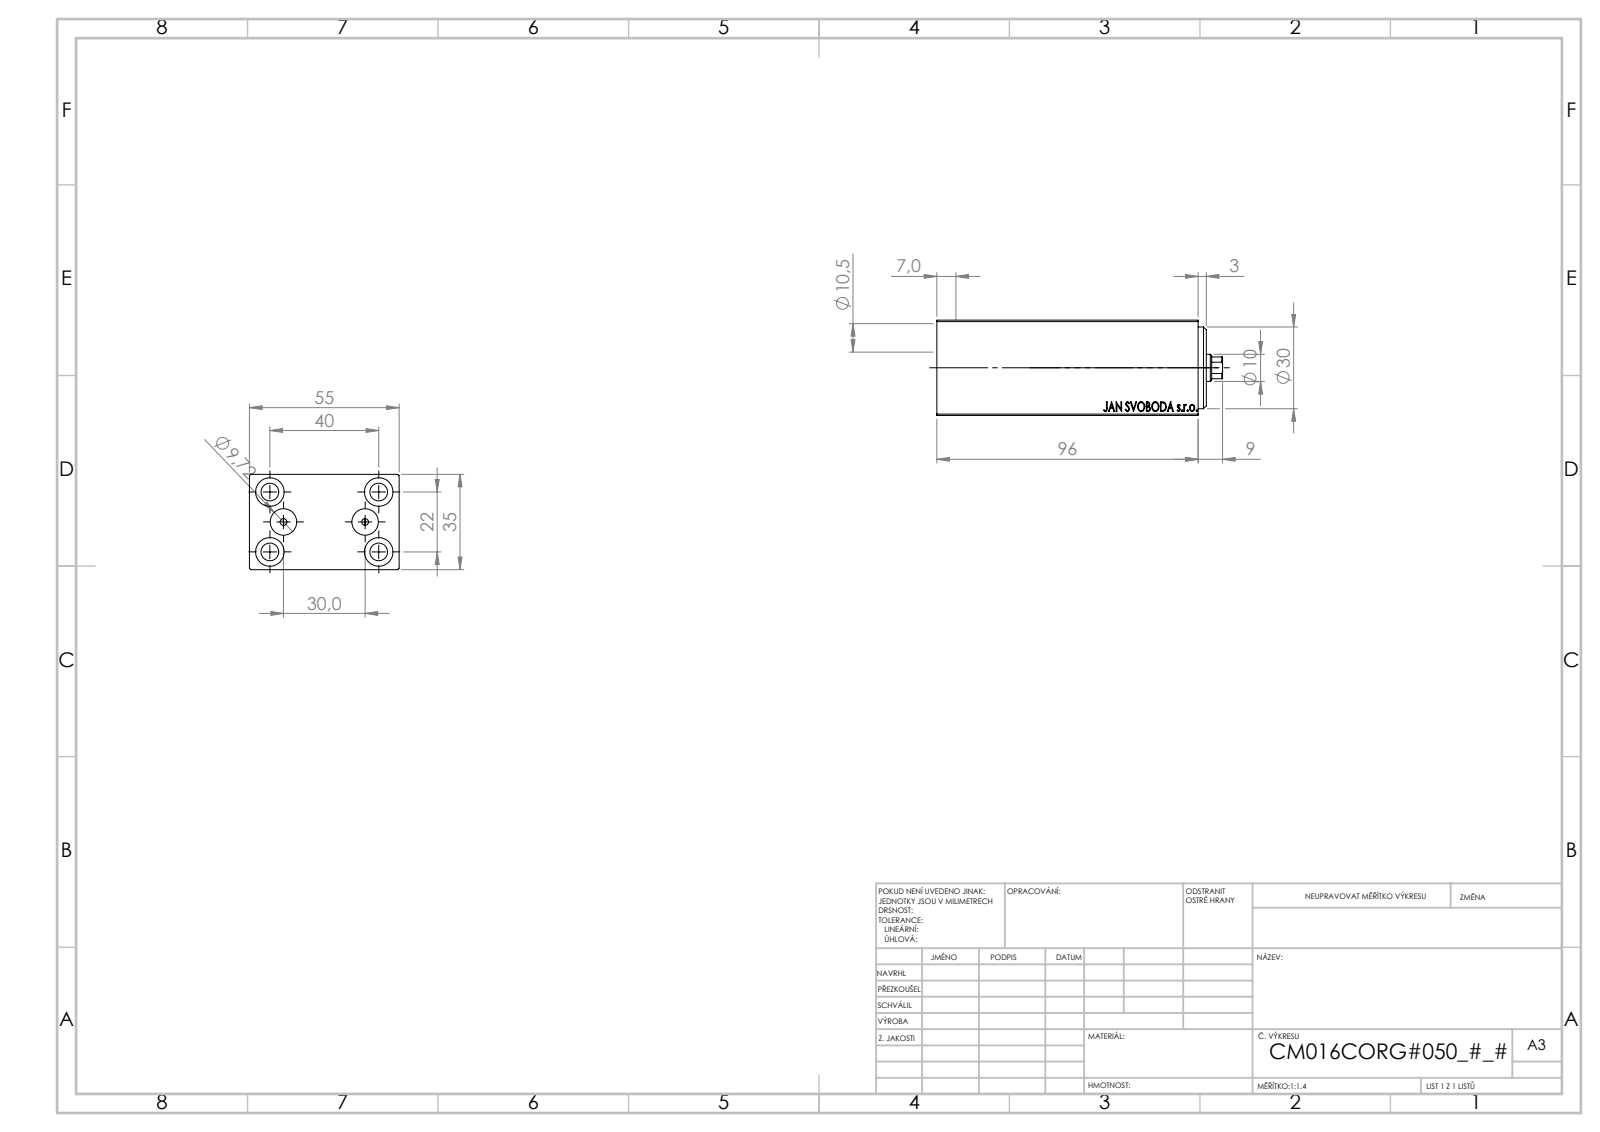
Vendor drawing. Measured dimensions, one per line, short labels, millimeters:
name: V450CM_C_VCP; V450CM_C_Body; V450CM_VC_B
written by: SolidWorks 2019 (CONFIG_CONTROL_DESIGN)
unit: mm
bodies: 3 solids, 861 faces (409 planar, 58 cylindrical, 394 other)
size: 105 × 55 × 35
volume: 162 712 mm³; area: 42 937 mm²
holes: 4× ⌀6.5, 4× ⌀10.5, 2× ⌀2.5, 2× ⌀9.72, 1× ⌀4.5, 1× ⌀10, 1× ⌀13.5, 1× ⌀14.5, 1× ⌀16, 1× ⌀18, 1× ⌀30
rounds: 1× R4.5
face distances: 35, 55, 5, 91, 96, 2, 3, 89, 86, 8
hole spacings: 12.08, 22.83, 36.69, 15, 22, 40, 45.65, 30
